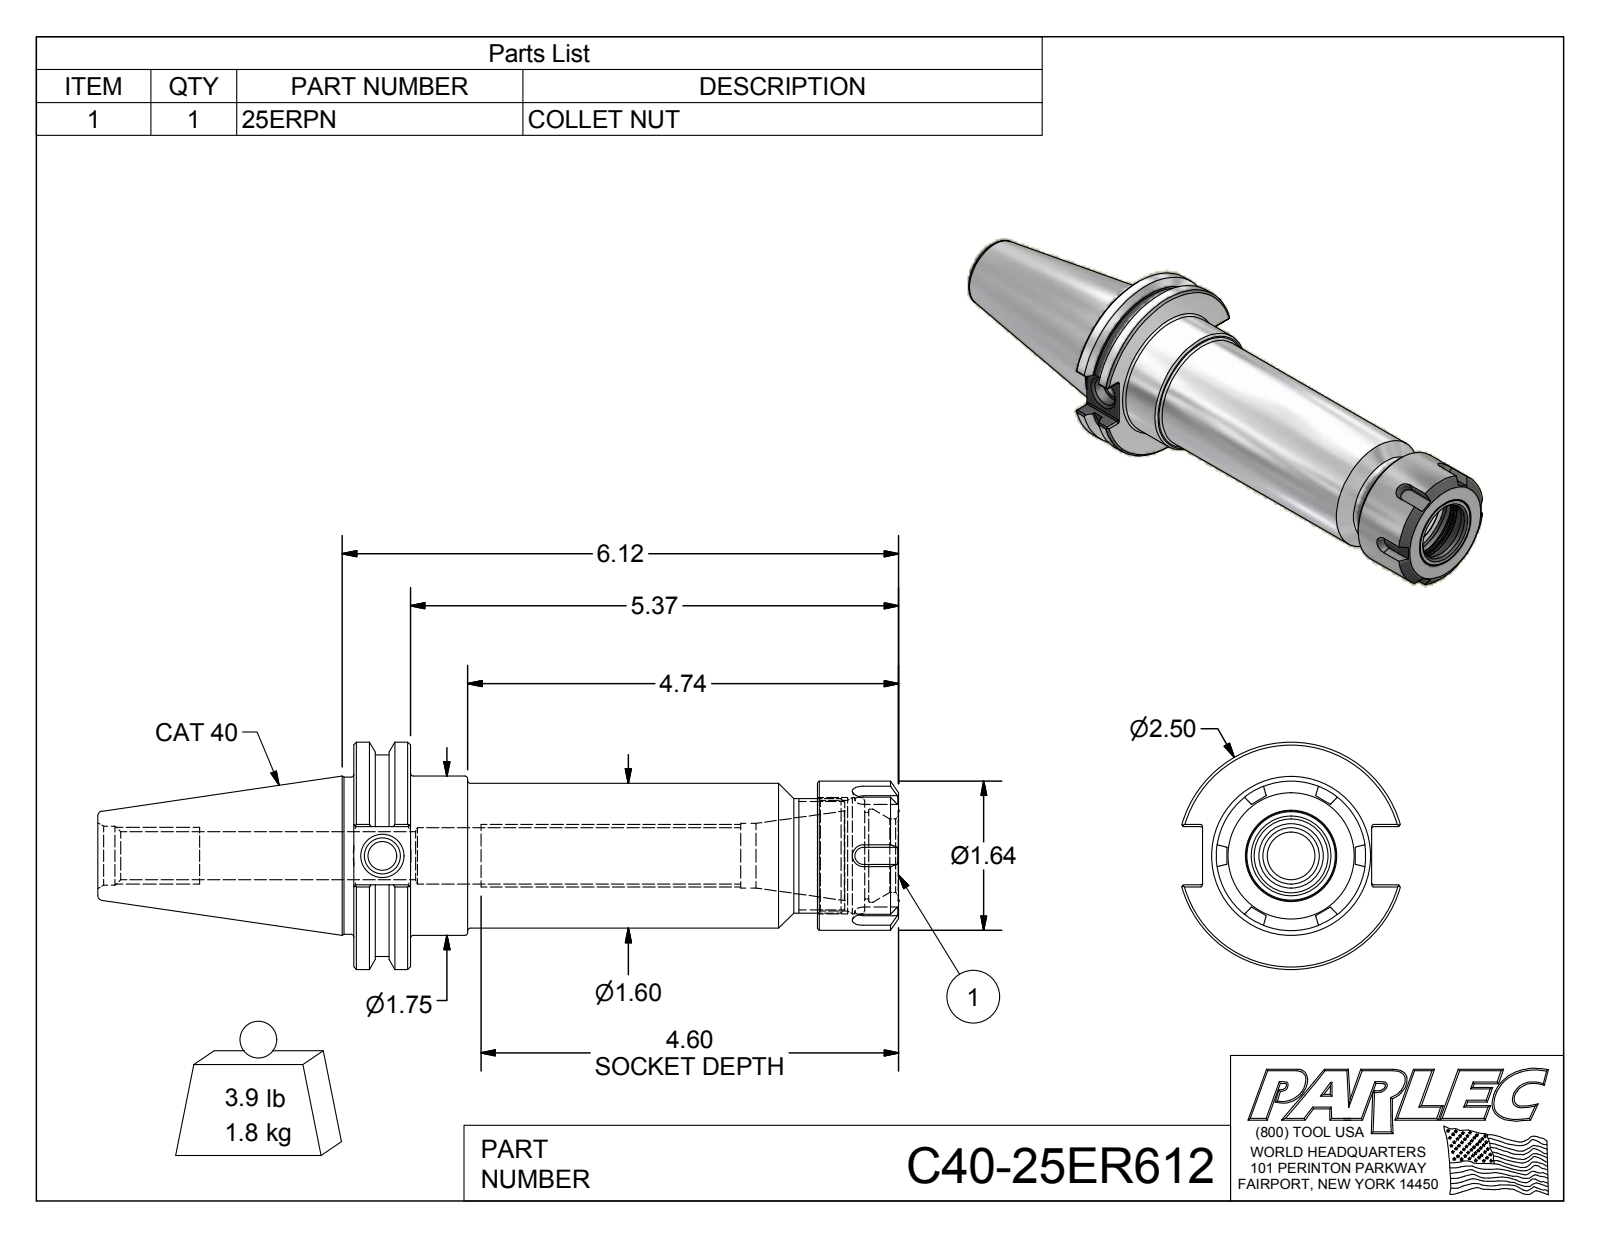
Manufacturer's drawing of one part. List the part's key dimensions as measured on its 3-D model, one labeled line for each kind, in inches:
Part name (STEP PRODUCT): C40-25ER612; C40-25ER6-1; 25ERPN
STEP written by: Autodesk Inventor 2012 (AUTOMOTIVE_DESIGN)
Units: inches
Bodies: 2 solids, 133 faces (56 planar, 34 cylindrical, 43 other)
Overall size (bounding box): 8.808 × 2.5 × 2.403
Volume: 14.65 in³ · Surface area: 74.66 in²
Round holes (diameter × count): ⌀0.315 ×1, ⌀0.399 ×1, ⌀0.527 ×1, ⌀0.62 ×1, ⌀0.648 ×1, ⌀0.71 ×1, ⌀0.811 ×1, ⌀0.95 ×1, ⌀1.027 ×1, ⌀1.217 ×1, ⌀1.28 ×1
Round bosses / shafts (diameter × count): ⌀2.5 ×1, ⌀2.219 ×1, ⌀1.75 ×1, ⌀1.73 ×1, ⌀1.643 ×1, ⌀1.595 ×1, ⌀1.26 ×1
Partial cylindrical surfaces — rounded edges, fillets, slot ends (radius × count): R0.02 ×12
Main face-to-face distances: 0.625, 5.995, 5.37, 5.102, 4.477, 0.893, 5.62, 4.995, 0.518, 0.375
